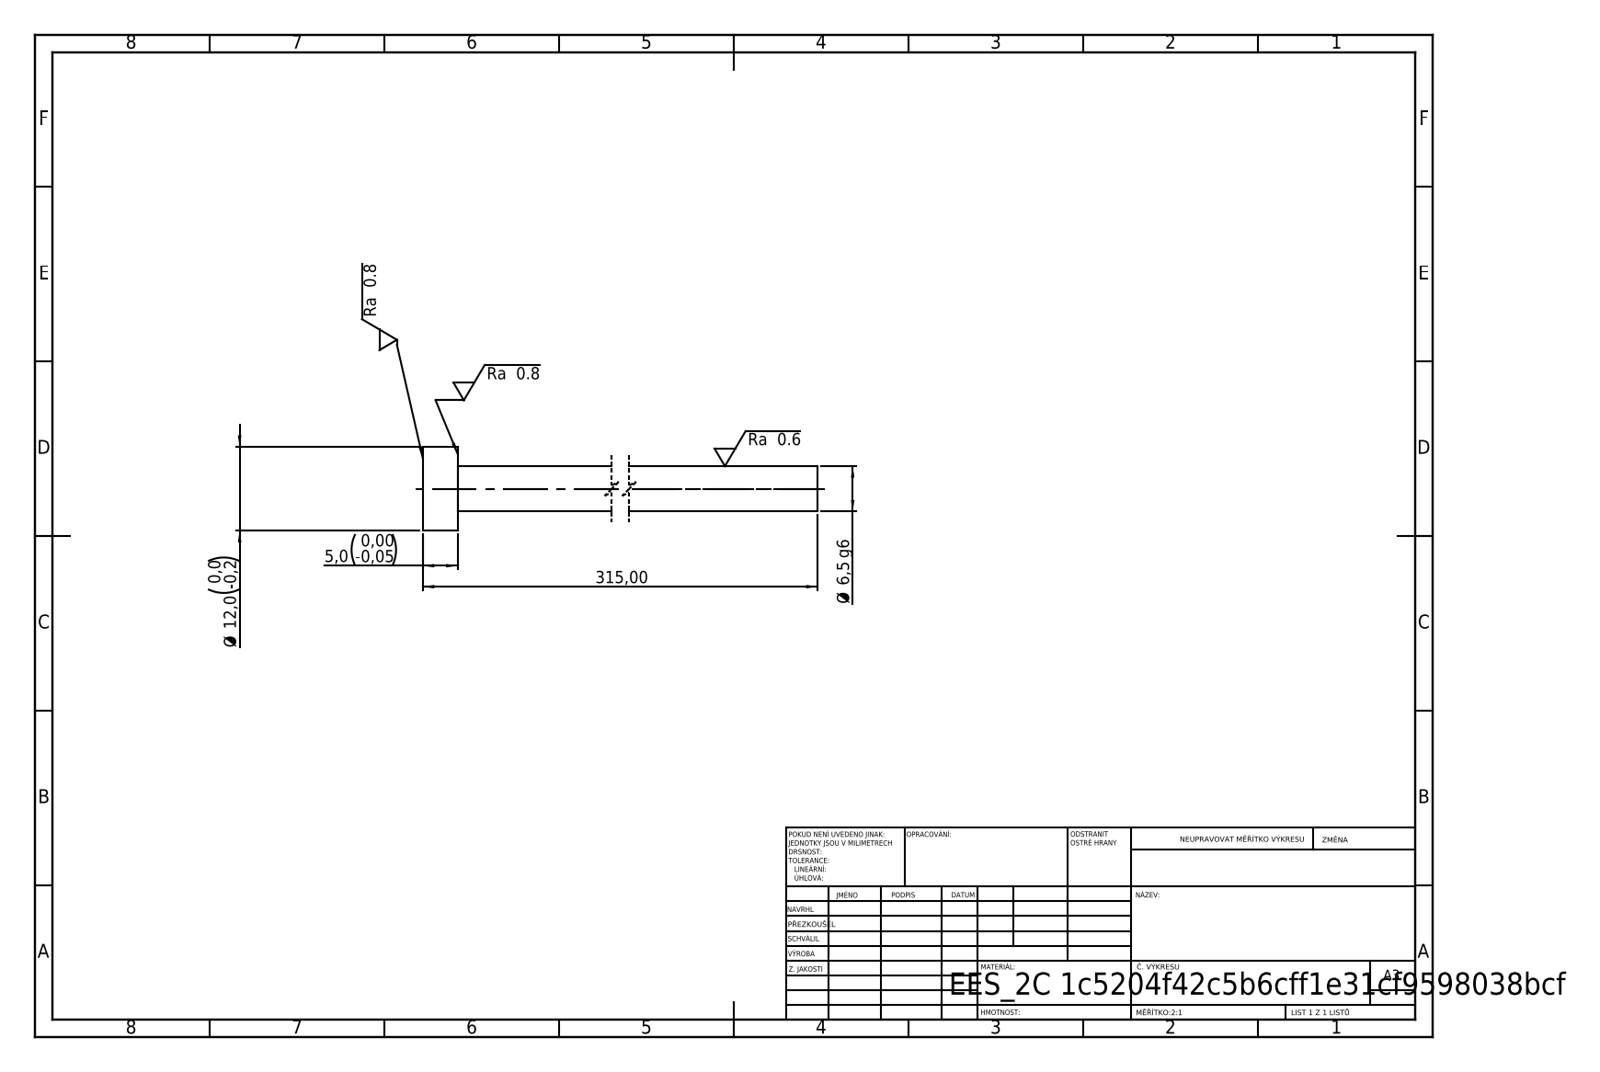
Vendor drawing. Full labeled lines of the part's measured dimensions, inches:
STEP written by: SolidWorks 2019 (CONFIG_CONTROL_DESIGN)
Units: inches
Bodies: 1 solid, 7 faces (3 planar, 4 cylindrical, 0 other)
Overall size (bounding box): 12.402 × 0.472 × 0.472
Volume: 0.662 in³ · Surface area: 10.45 in²
Round bosses / shafts (diameter × count): ⌀0.472 ×1, ⌀0.256 ×1
Main face-to-face distances: 0.197, 12.402, 12.205
